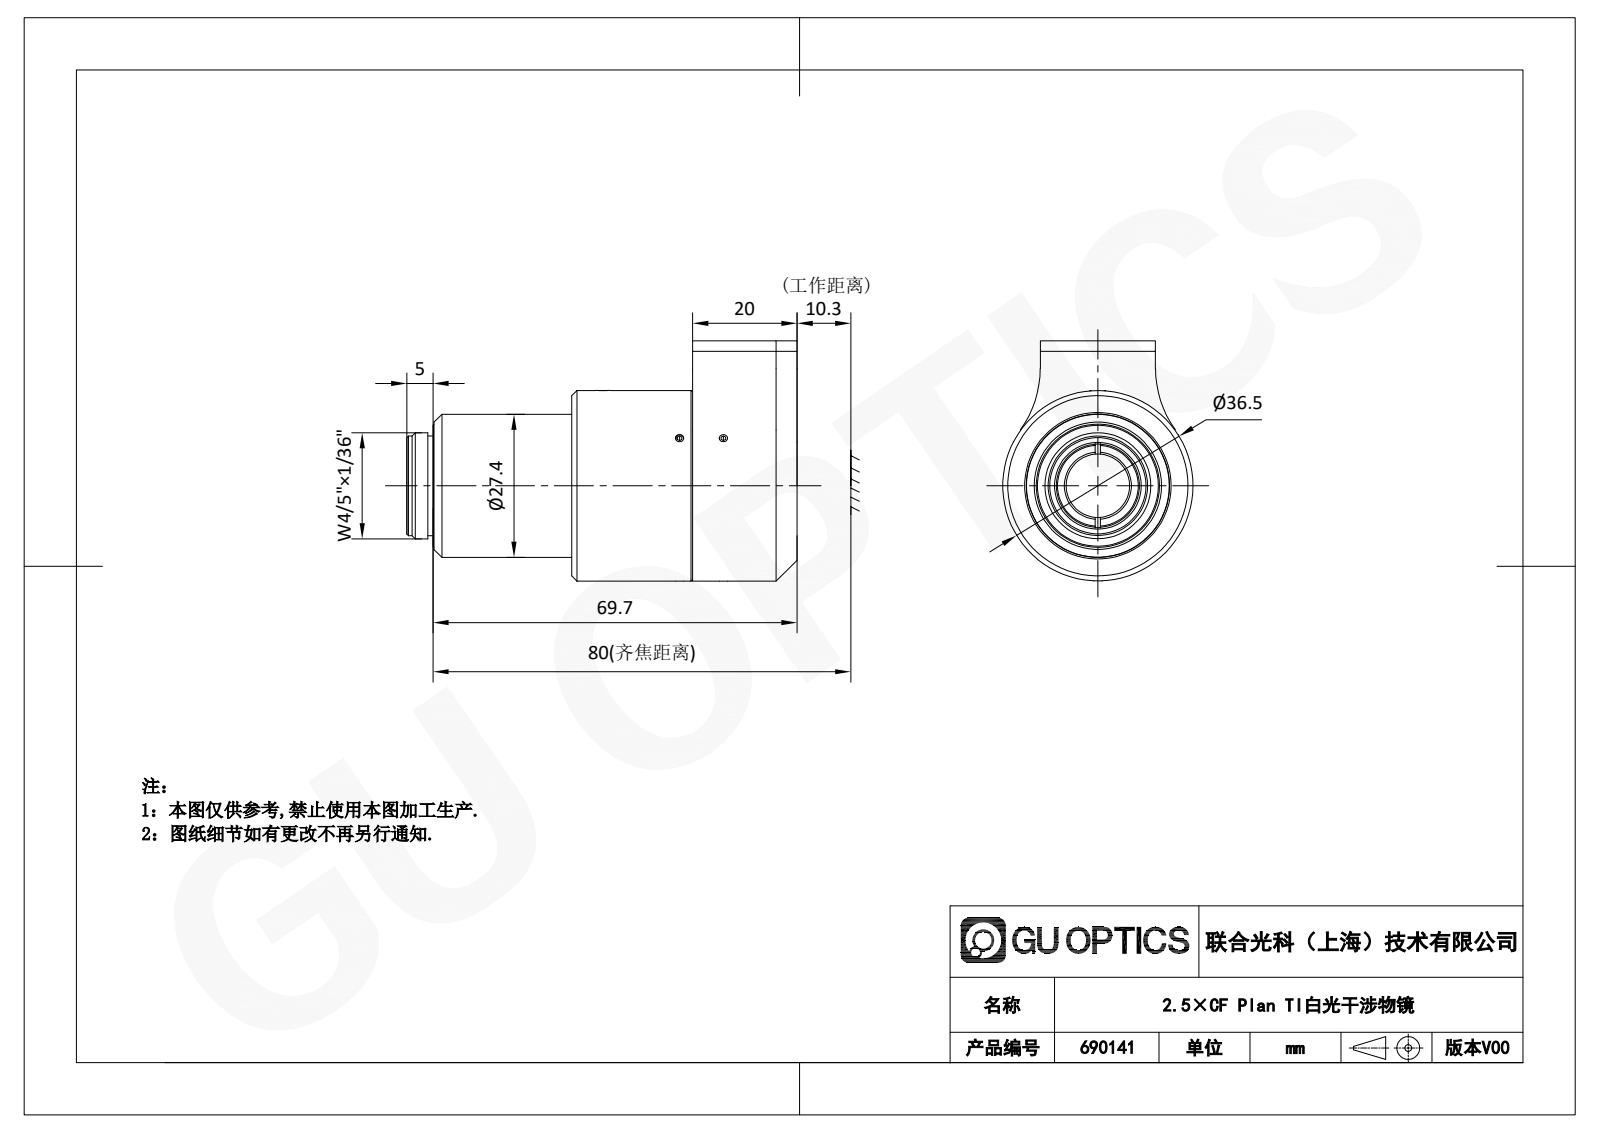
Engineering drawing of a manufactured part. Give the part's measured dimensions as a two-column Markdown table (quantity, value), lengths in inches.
| quantity | value |
| --- | --- |
| part name | X2_87BA9489_X0_ GB_T 819.1 M1.6 x 3(1); X2_87BA9489_X0_ GB_T 819.1 M1.6 x 4(1); X2_540E51499611_X0; X2_5E726D89955C5EA7_X0 (+8 more) |
| STEP written by | SolidWorks 2020 (CONFIG_CONTROL_DESIGN) |
| units | inches |
| bodies | 20 solids, 392 faces (181 planar, 84 cylindrical, 127 other) |
| overall size | 2.941 × 1.811 × 1.437 |
| volume | 2.254 in³ |
| surface area | 48.28 in² |
| round holes (diameter × count) | 0.048 × 5, 0.062 × 3, 0.062 × 3, 0.118 × 3, 0.048 × 2, 0.63 × 2, 0.449 × 1, 0.472 × 1, 0.48 × 1, 0.543 × 1, 0.78 × 1, 0.787 × 1 |
| round bosses / shafts (diameter × count) | 0.079 × 6, 0.063 × 6, 0.118 × 3, 0.054 × 3, 1.437 × 1, 1.299 × 1, 0.965 × 1, 0.937 × 1 |
| partial cylindrical surfaces (radius × count) | 0.049 × 4, 0.787 × 2 |
| main face-to-face distances | 0.843, 0.702, 1.545, 0.079, 0.315, 1.23, 0.528, 1.315, 1.63, 0.085 |
| hole center spacings | 0.266, 0.331, 0.322, 0.335, 0.382, 0.459, 0.491, 0.538 |
